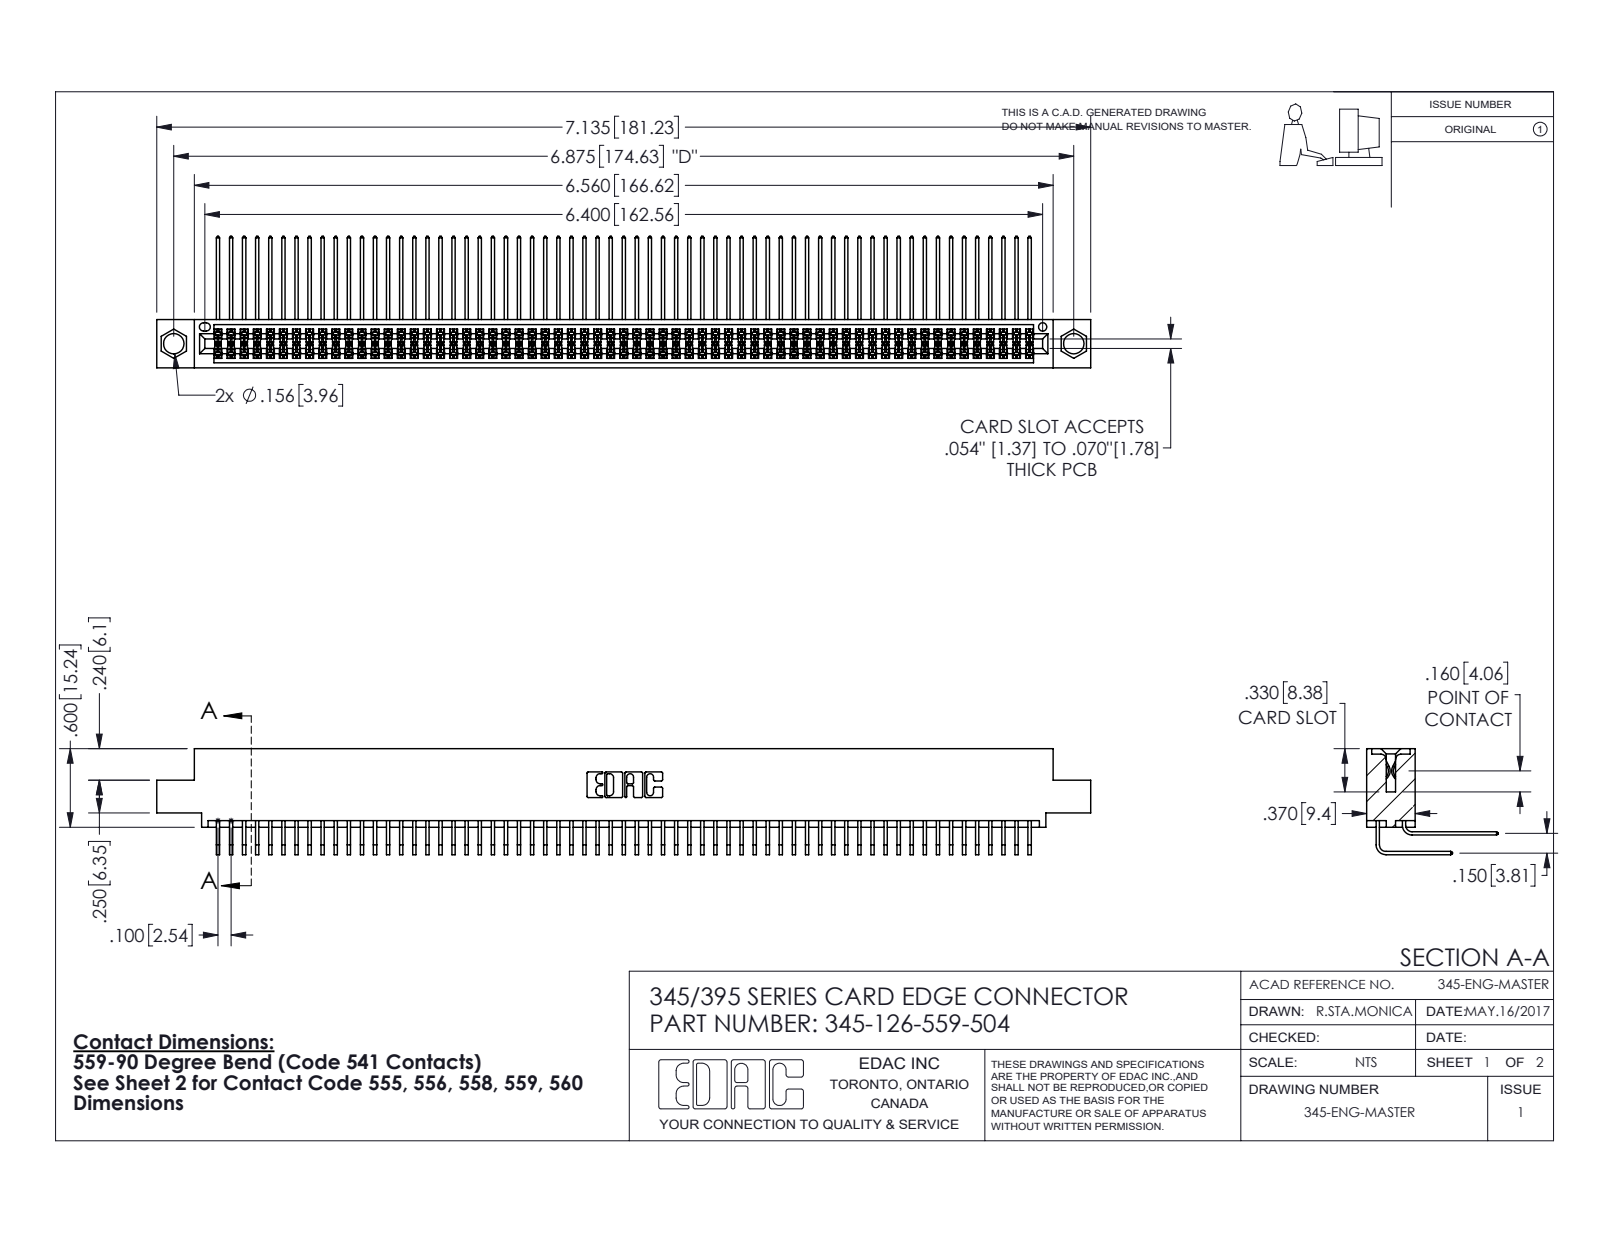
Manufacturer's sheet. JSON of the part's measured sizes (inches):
{"part_name": "345-292-001_558 559 Tail - 1; 345-126-559-504; 345-292-001_559 Tail - 2; 345 Part_0.110 Offset - 0.156 Dia-TI", "step_written_by": "SolidWorks 2020 (CONFIG_CONTROL_DESIGN)", "units": "inches", "bodies": {"solids": 127, "faces": 6696, "planar": 4508, "cylindrical": 2188, "other": 0}, "overall_size": [7.135, 1.005, 0.809], "volume_in3": 1.12, "surface_area_in2": 47.88, "round_holes": [[0.156, 2], [0.064, 1]], "partial_cylinders_radius": [[0.006, 189], [0.01, 22], [0.007, 6], [0.031, 6], [0.026, 3], [0.014, 2], [0.019, 2], [0.022, 2]], "face_to_face_distances": [0.072, 0.298, 0.2, 0.37, 0.098, 0.272, 0.025, 0.225, 0.175, 0.15], "hole_center_spacings": [0.27, 6.639, 6.875]}
